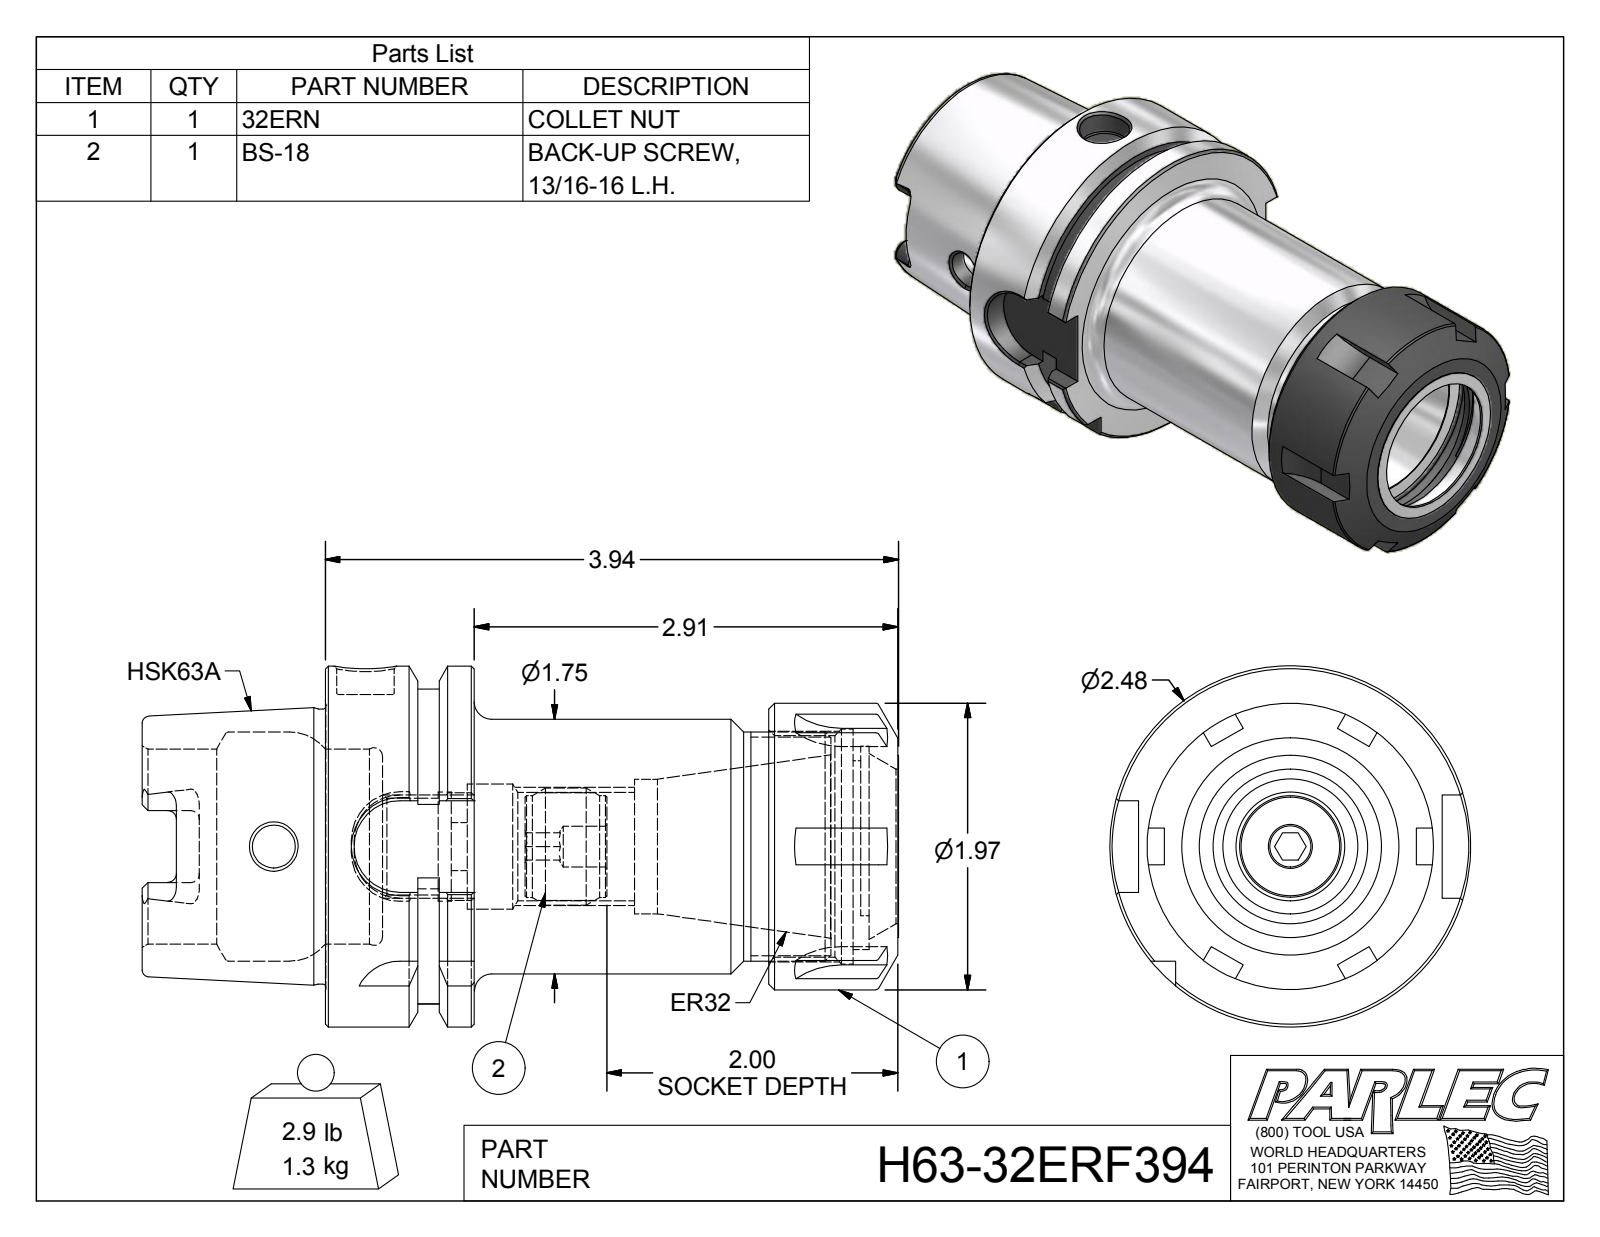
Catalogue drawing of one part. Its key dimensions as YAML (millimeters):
part_name: "H63-32ERF394; 32ERN; H63-32ER4-1; BS-18"
step_written_by: "Autodesk Inventor 2012 (AUTOMOTIVE_DESIGN)"
units: millimeters
bodies: {solids: 3, faces: 207, planar: 85, cylindrical: 54, other: 68}
overall_size: [132.1, 63, 63]
volume: 165200
surface_area: 45650
round_holes:
  - {diameter: 7.1, count: 1}
  - {diameter: 7.5, count: 1}
  - {diameter: 8.4, count: 1}
  - {diameter: 10, count: 1}
  - {diameter: 16.9, count: 1}
  - {diameter: 18.9, count: 1}
  - {diameter: 19, count: 1}
  - {diameter: 21.9, count: 1}
  - {diameter: 23.5, count: 1}
  - {diameter: 27, count: 1}
  - {diameter: 33, count: 1}
  - {diameter: 34, count: 1}
round_bosses_or_shafts:
  - {diameter: 63, count: 1}
  - {diameter: 50, count: 1}
  - {diameter: 48, count: 1}
  - {diameter: 44.5, count: 1}
  - {diameter: 31.8, count: 1}
  - {diameter: 20.4, count: 1}
  - {diameter: 17.8, count: 1}
partial_cylinders:
  - {radius: 1.5, count: 6}
  - {radius: 12.7, count: 6}
  - {radius: 2.9, count: 4}
  - {radius: 8, count: 4}
  - {radius: 17.5, count: 1}
  - {radius: 27.5, count: 1}
face_to_face_distances: [26, 6.1, 9.9, 10, 16, 77.4, 67.5, 51.5, 92.2, 82.1]
hole_center_spacings: [1.5]
